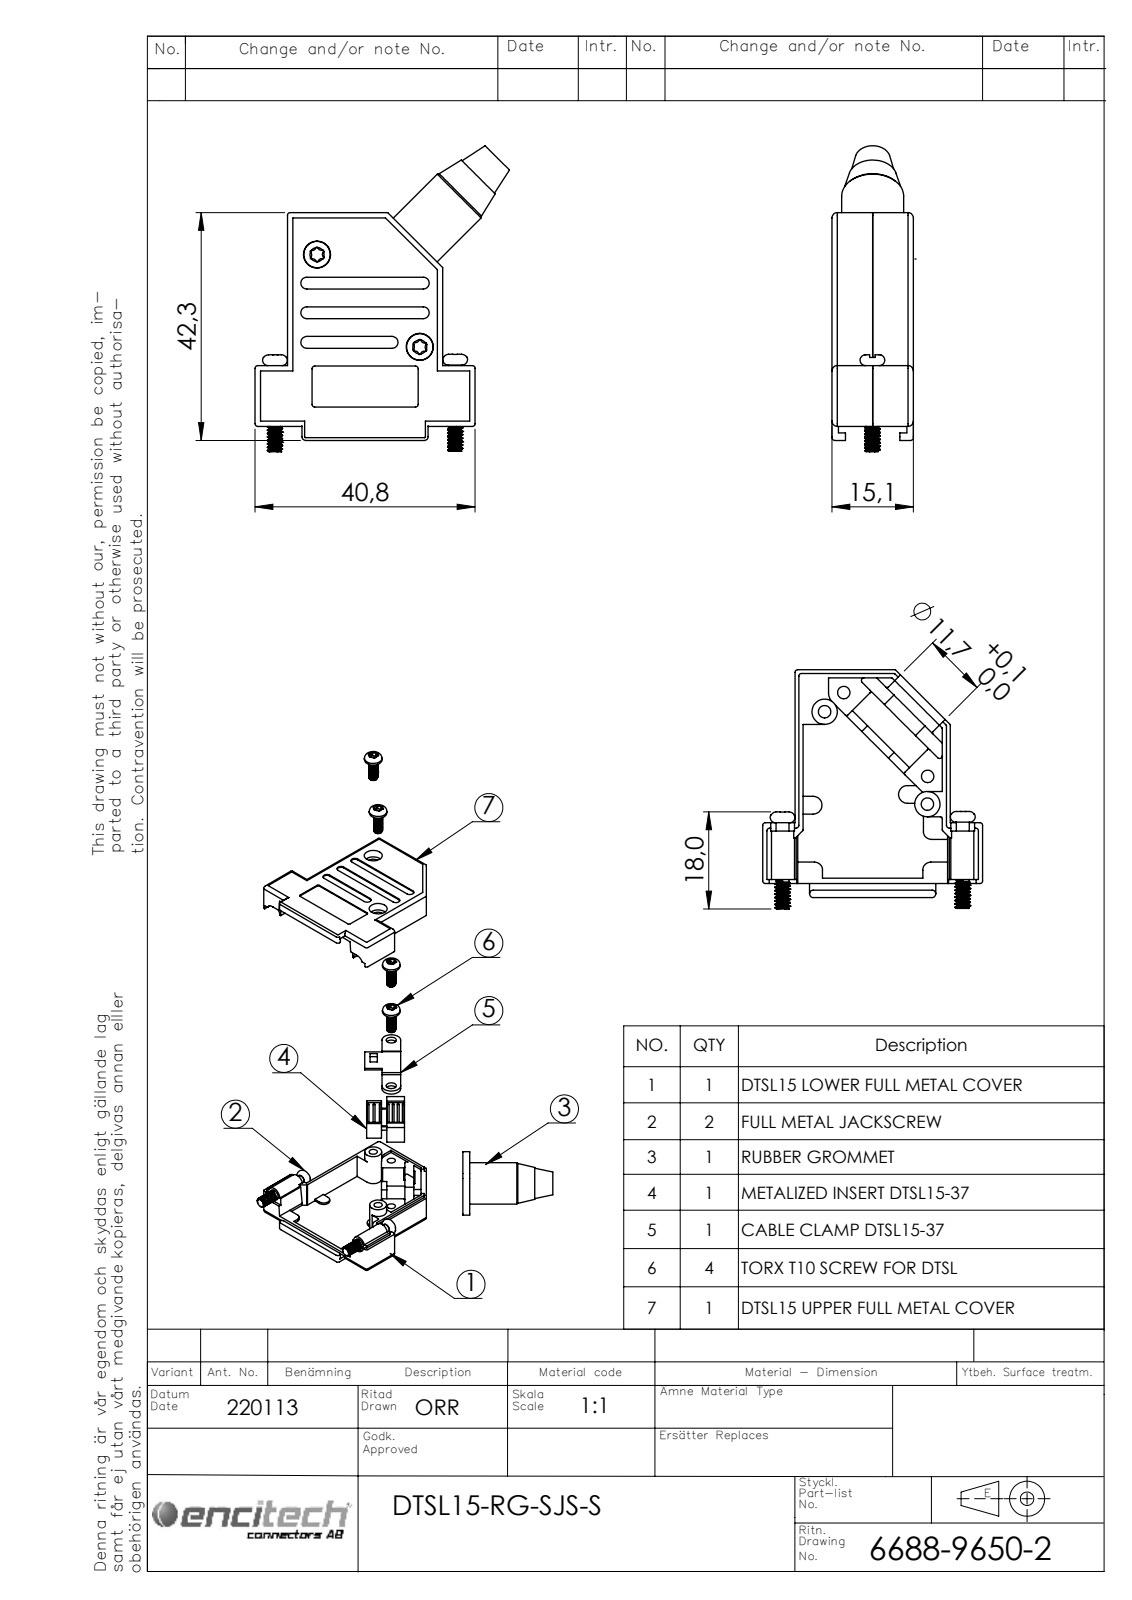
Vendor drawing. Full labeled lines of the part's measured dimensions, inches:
Part name (STEP PRODUCT): 6844-0104-01; 6805-0208-12; 6560-0218-32; 6826-0145-01 (+4 more)
STEP written by: SolidWorks 2021 (AUTOMOTIVE_DESIGN)
Units: inches
Bodies: 15 solids, 970 faces (382 planar, 500 cylindrical, 88 other)
Overall size (bounding box): 2.236 × 1.858 × 0.606
Volume: 0.557 in³ · Surface area: 20.47 in²
Round holes (diameter × count): ⌀0.091 ×4, ⌀0.11 ×4, ⌀0.122 ×2, ⌀0.197 ×2, ⌀0.173 ×1, ⌀0.354 ×1, ⌀0.461 ×1
Round bosses / shafts (diameter × count): ⌀0.193 ×4, ⌀0.098 ×4, ⌀0.224 ×2, ⌀0.185 ×2, ⌀0.11 ×2, ⌀0.094 ×2, ⌀0.453 ×1, ⌀0.437 ×1
Partial cylindrical surfaces — rounded edges, fillets, slot ends (radius × count): R0.028 ×26, R0.007 ×24, R0.02 ×24, R0.039 ×22, R0.012 ×10, R0.043 ×7, R0.01 ×4, R0.059 ×4
Main face-to-face distances: 0.053, 0.541, 0.594, 0.488, 0.059, 0.041, 0.244, 0.297, 0.583, 0.53
Hole centre spacings: 0.198, 0.202, 0.203, 0.867, 0.889, 1.009, 1.009, 1.018
